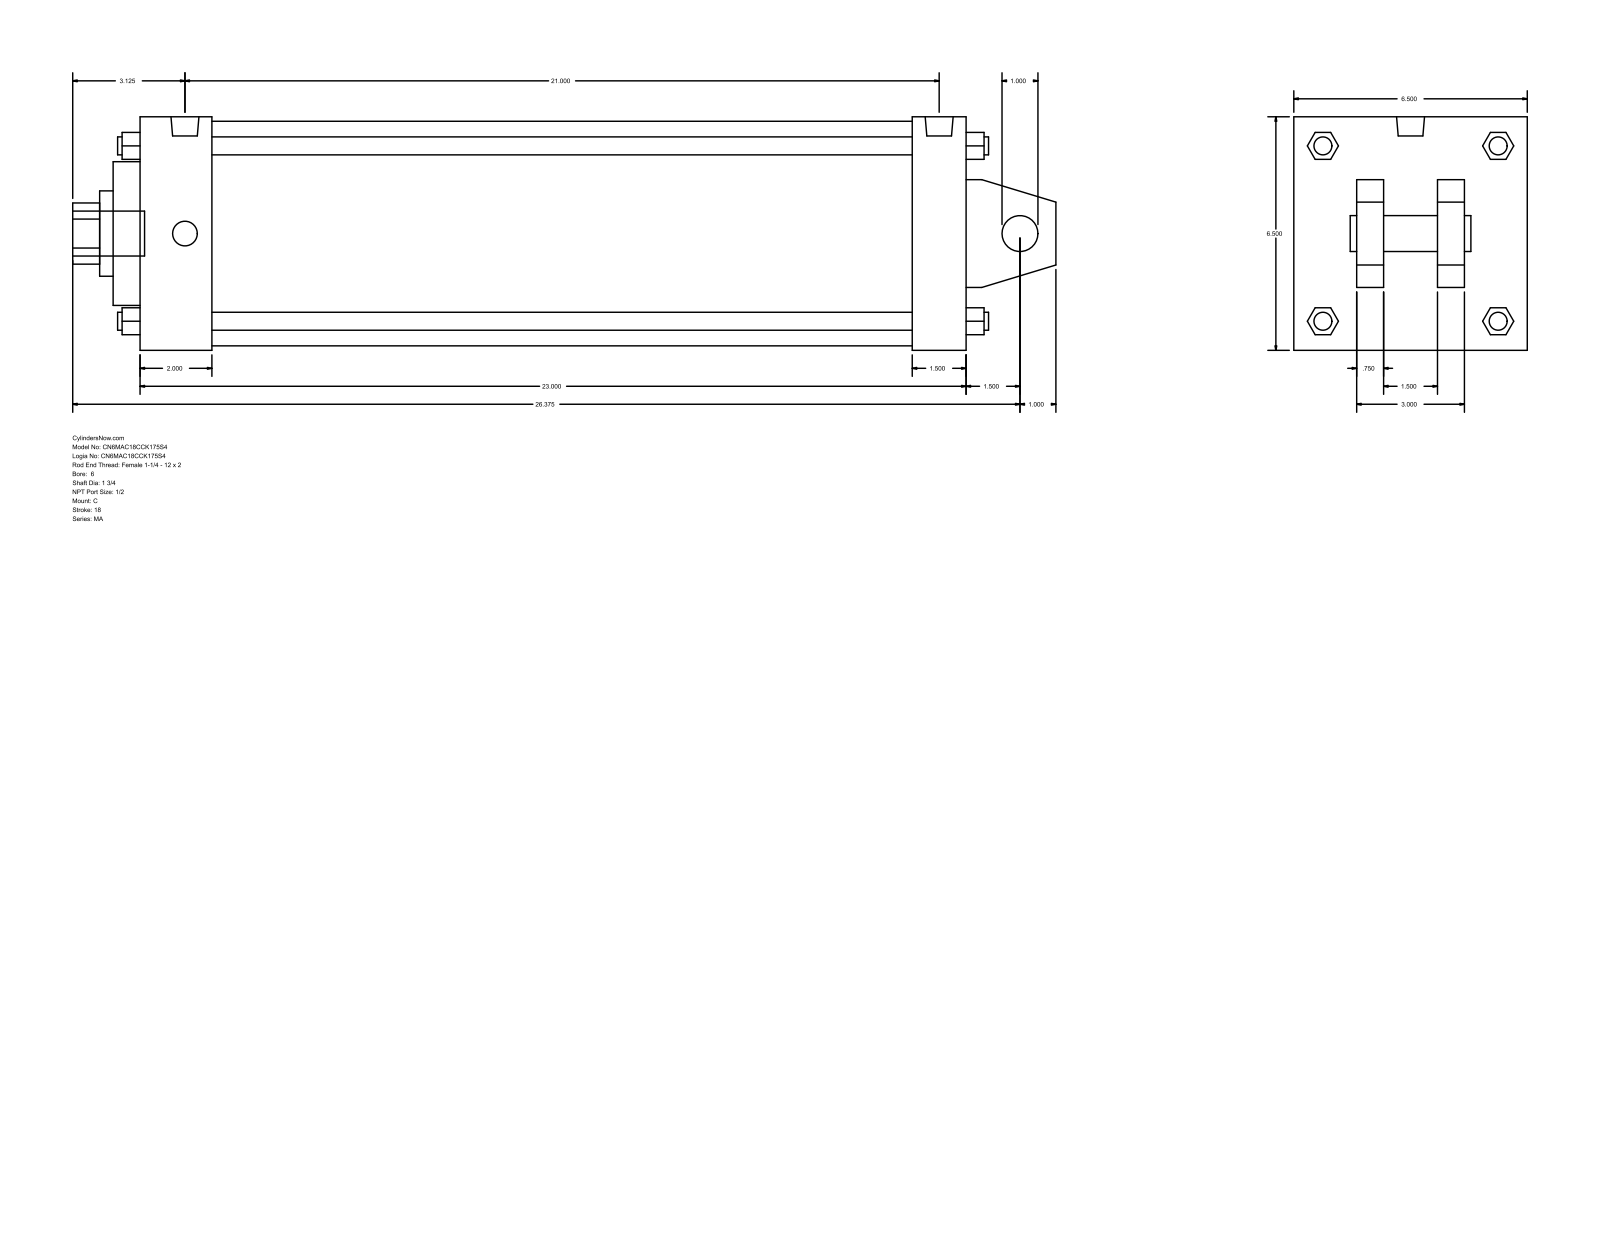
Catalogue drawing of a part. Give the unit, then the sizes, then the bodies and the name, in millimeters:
Units: millimetres
Overall size (bounding box): 695.33 × 165.1 × 165.1
Round holes (diameter × count): ⌀25.4 ×1, ⌀44.45 ×1, ⌀60.33 ×1, ⌀101.6 ×1, ⌀158.75 ×1
Round bosses / shafts (diameter × count): ⌀17.46 ×4, ⌀12.7 ×4, ⌀19.77 ×2, ⌀31.75 ×1
Partial cylindrical surfaces — rounded edges, fillets, slot ends (radius × count): R21.63 ×1
Main face-to-face distances: 165.1, 584.21, 19.05, 38.1, 63.5, 101.6, 44.45, 120.65, 57.15, 50.8
Bodies: 0 solids, 141 faces (109 planar, 32 cylindrical, 0 other)
Part name (STEP PRODUCT): MA_C__0600_1.75
STEP written by: GSSL Pune (CONFIG_CONTROL_DESIGN)
